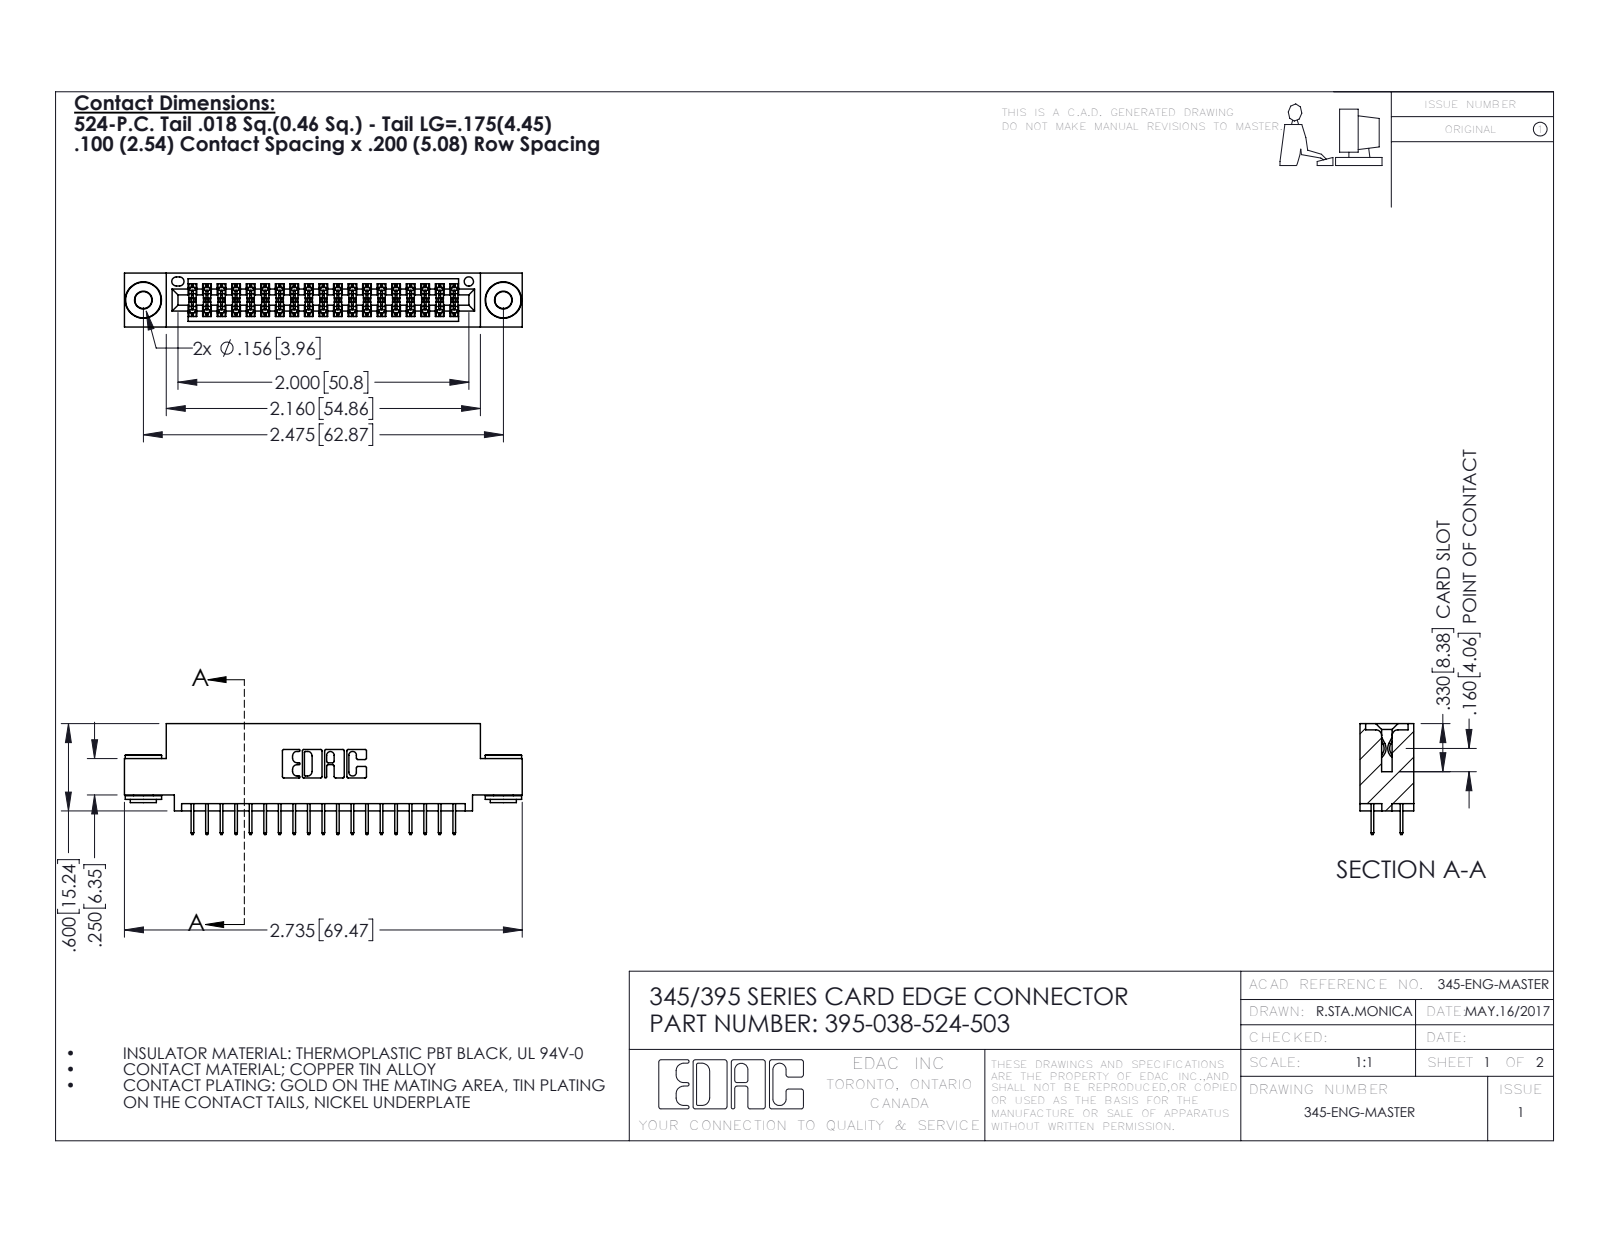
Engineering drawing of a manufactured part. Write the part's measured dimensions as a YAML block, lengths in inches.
part_name: "345-250-002_345-250-002-102; 395-038-524-503; 345 Part_0.110 Offset - 0.156 Dia-TH; 345-292-001_345-293-124"
step_written_by: "SolidWorks 2016 (CONFIG_CONTROL_DESIGN)"
units: inches
bodies: {solids: 41, faces: 2220, planar: 1576, cylindrical: 636, other: 8}
overall_size: [2.735, 0.762, 0.37]
volume: 0.392
surface_area: 14.25
round_holes:
  - {diameter: 0.116, count: 2}
  - {diameter: 0.156, count: 2}
  - {diameter: 0.064, count: 1}
round_bosses_or_shafts:
  - {diameter: 0.25, count: 2}
  - {diameter: 0.18, count: 2}
  - {diameter: 0.136, count: 2}
partial_cylinders:
  - {radius: 0.006, count: 57}
  - {radius: 0.01, count: 22}
  - {radius: 0.007, count: 6}
  - {radius: 0.031, count: 6}
  - {radius: 0.026, count: 3}
  - {radius: 0.014, count: 2}
  - {radius: 0.019, count: 2}
  - {radius: 0.022, count: 2}
face_to_face_distances: [0.072, 0.298, 0.2, 0.37, 0.025, 0.098, 0.272, 0.225, 0.072, 0.175]
hole_center_spacings: [0.27, 2.241, 2.475]
